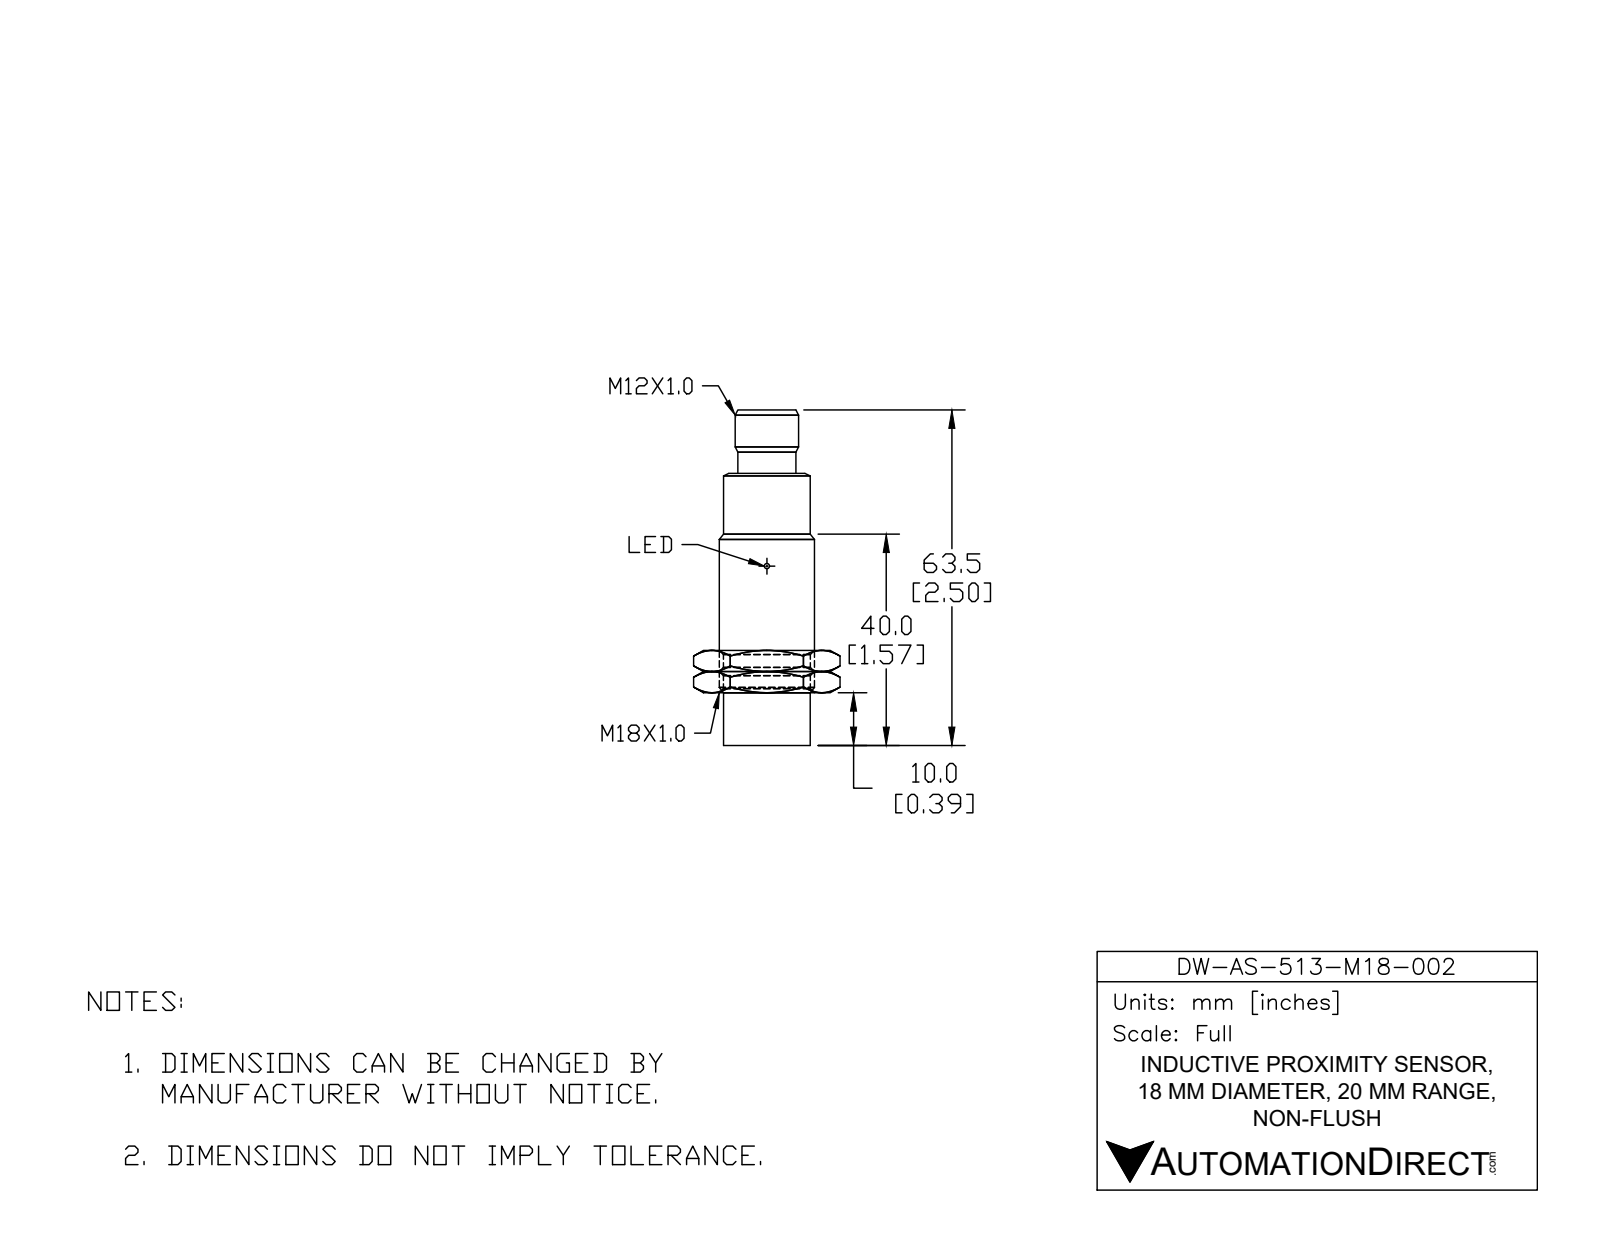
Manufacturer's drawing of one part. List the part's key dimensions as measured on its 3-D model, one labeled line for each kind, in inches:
Part name (STEP PRODUCT): DW-AS-513-M18-002
STEP written by: SolidWorks 2017 (AUTOMOTIVE_DESIGN)
Units: inches
Bodies: 1 solid, 36 faces (13 planar, 14 cylindrical, 9 other)
Overall size (bounding box): 2.502 × 0.709 × 0.709
Volume: 0.779 in³ · Surface area: 6.427 in²
Round holes (diameter × count): ⌀0.12 ×2, ⌀0.335 ×1
Round bosses / shafts (diameter × count): ⌀0.043 ×3, ⌀0.709 ×1, ⌀0.65 ×1, ⌀0.646 ×1, ⌀0.472 ×1, ⌀0.415 ×1
Partial cylindrical surfaces — rounded edges, fillets, slot ends (radius × count): R0.019 ×2, R0.022 ×1
Main face-to-face distances: 1.988, 2.159, 0.171, 2.502, 0.514, 0.343, 1.654, 0.335, 0.506, 0.848
